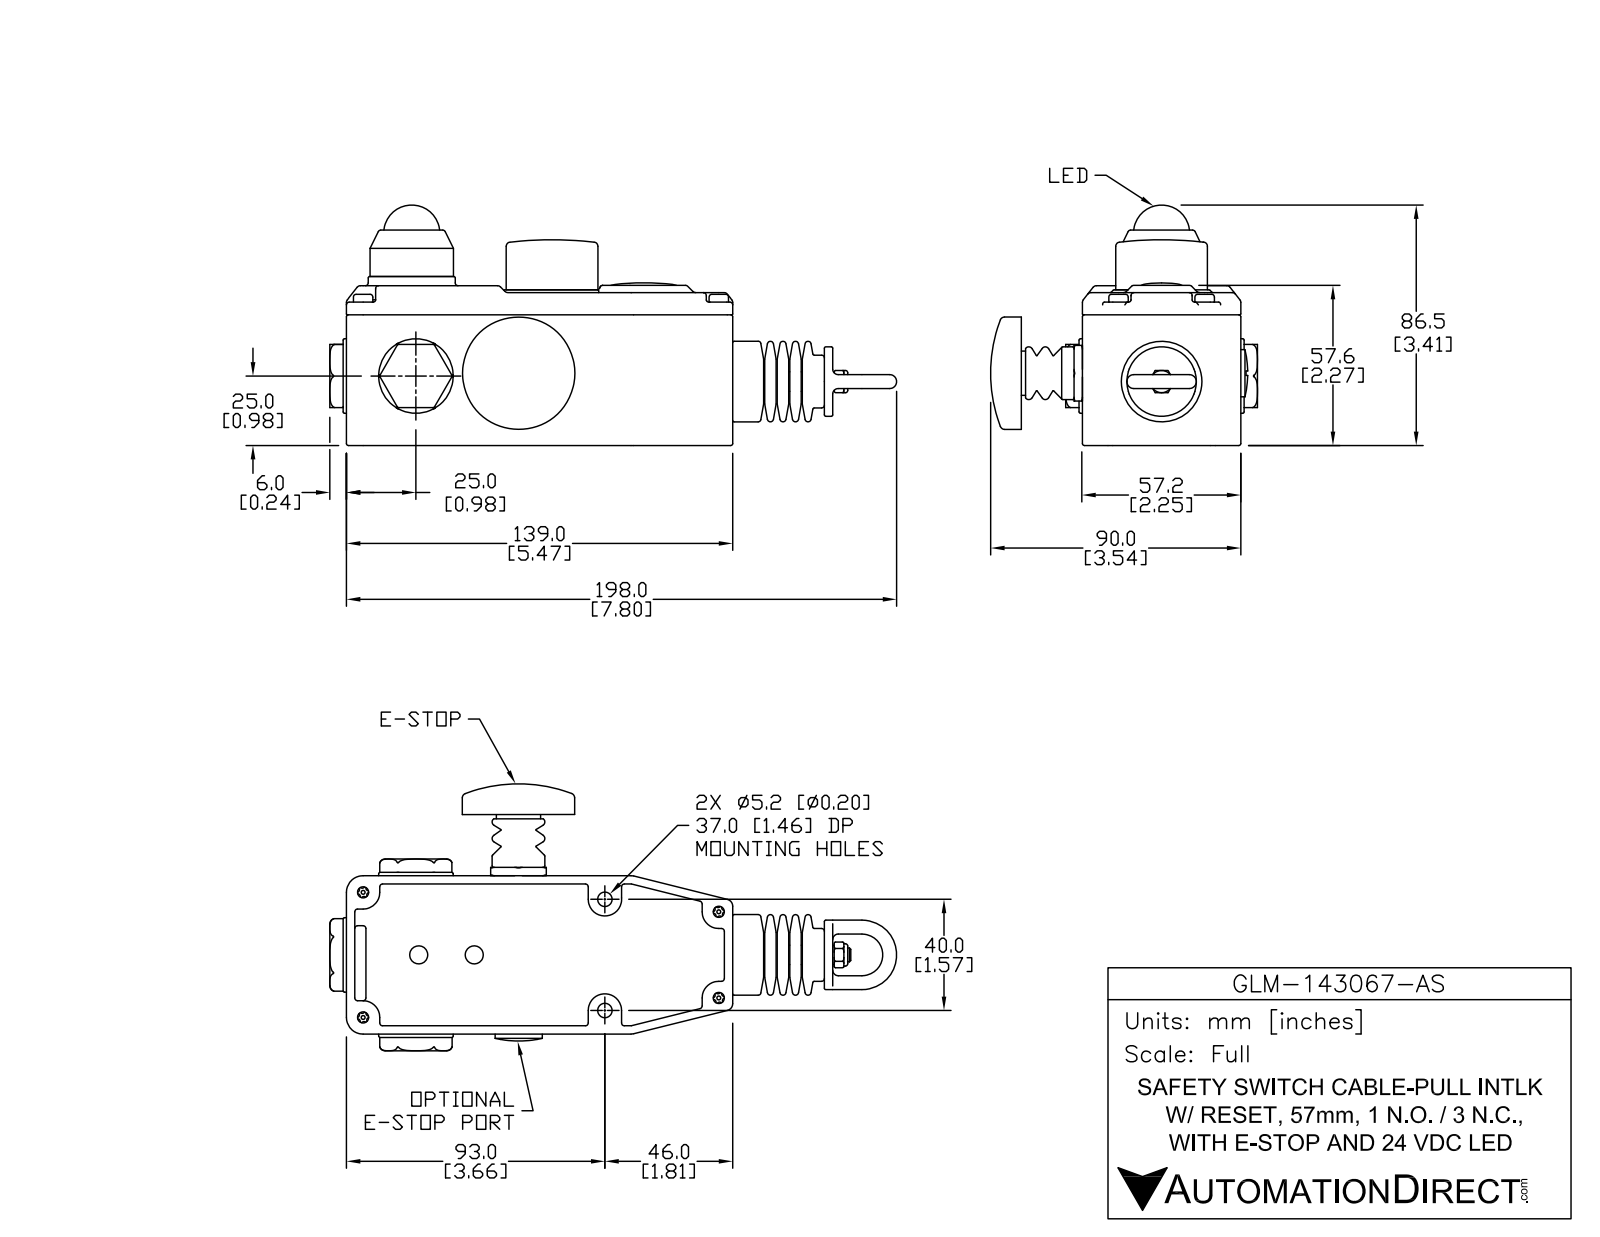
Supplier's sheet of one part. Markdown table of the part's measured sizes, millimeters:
| quantity | value |
| --- | --- |
| part name | GLM-143067-AS |
| STEP written by | SolidWorks 2013 (AUTOMOTIVE_DESIGN) |
| units | millimeters |
| bodies | 1 solid, 442 faces (132 planar, 150 cylindrical, 160 other) |
| overall size | 204 × 96.5 × 83.91 |
| volume | 486 361 mm³ |
| surface area | 58 860 mm² |
| round holes (diameter × count) | 4 × 4, 5.2 × 2, 21 × 1, 34 × 1 |
| round bosses / shafts (diameter × count) | 7 × 5, 26.8 × 2, 5 × 2, 40 × 1, 33 × 1, 31.3 × 1, 30 × 1, 29 × 1 |
| partial cylindrical surfaces (radius × count) | 0.16 × 31, 0.5 × 31, 1 × 4, 5.2 × 4, 7 × 2, 13 × 2 |
| main face-to-face distances | 57.2, 54.68, 57.18, 2.5, 57.5, 55, 0.32, 139, 6.3, 63.5 |
| hole center spacings | 28.53, 28.66, 31, 40, 41.24, 41.25, 45, 54.21 |
